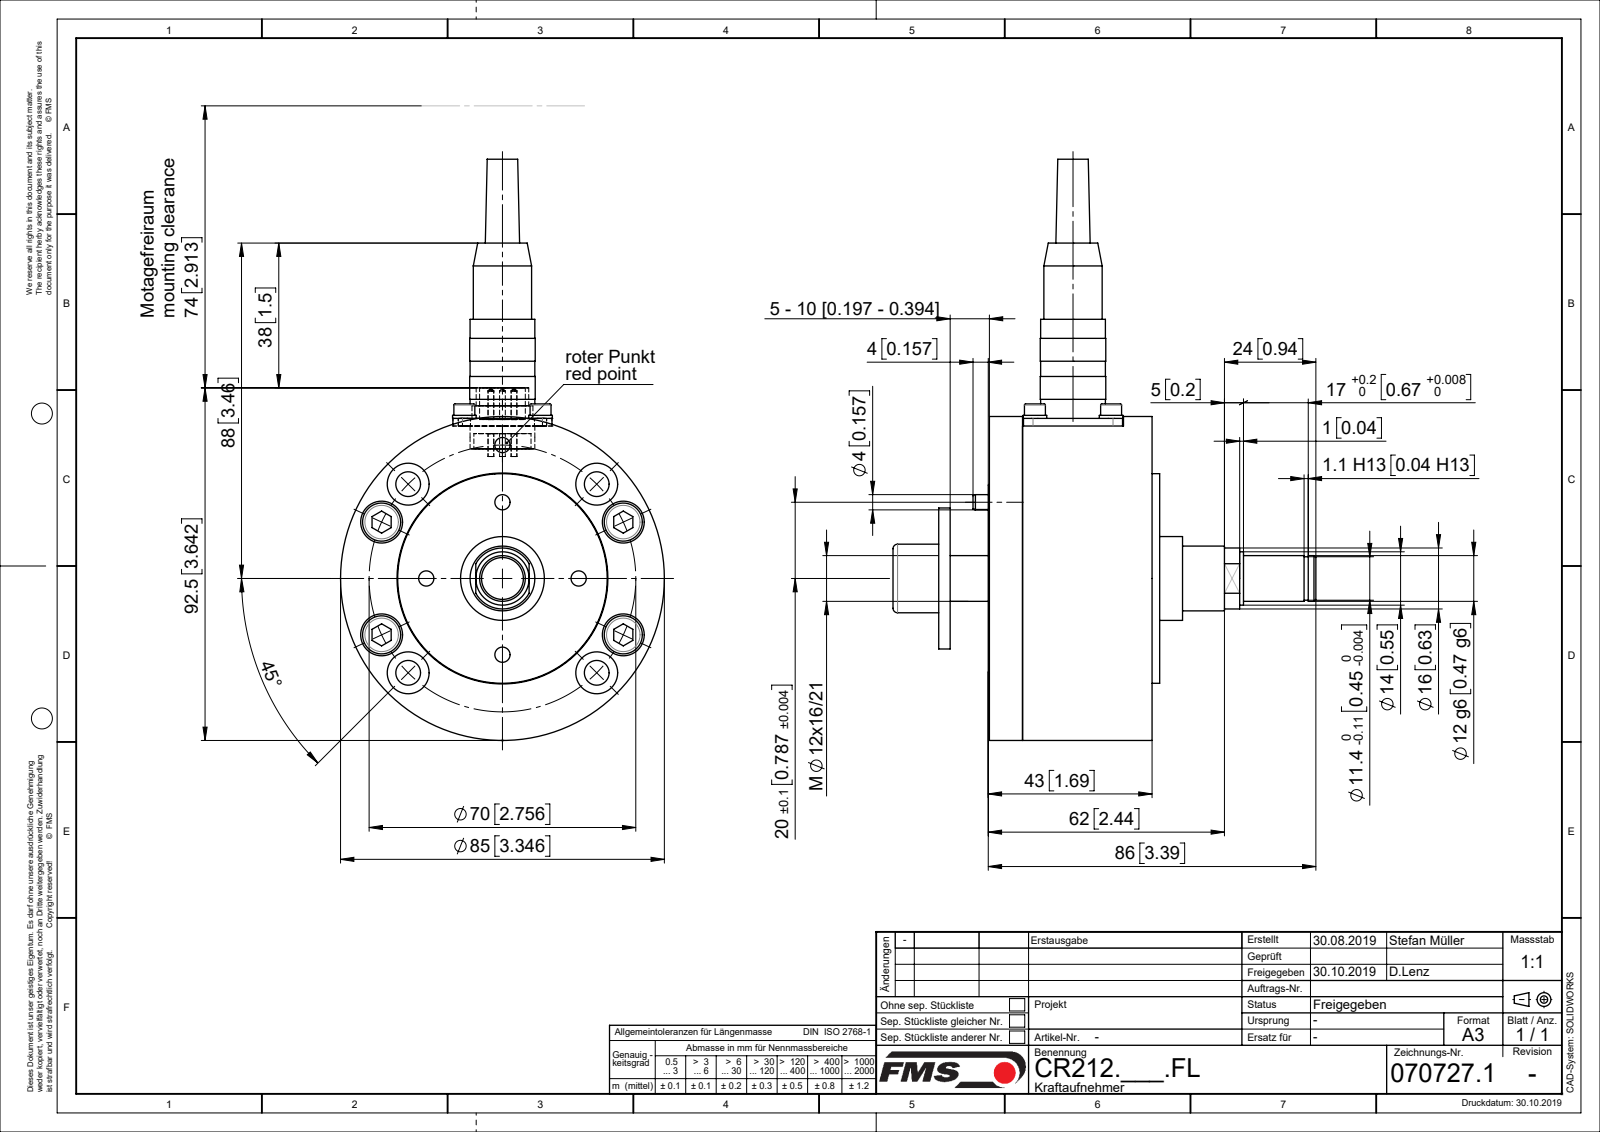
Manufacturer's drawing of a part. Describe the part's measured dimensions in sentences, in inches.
The part is named "ZEICHNUNG5; C0707271; C0709081; C0612056 (+8 more)". Its 3-D file was written by "Mechanical Desktop 2009 (CONFIG_CONTROL_DESIGN)". It is 26 solids with 485 faces: 150 planar, 249 cylindrical and 86 other. Overall it measures 6.004 by 4.409 by 3.346 inches. Its volume is 13.48 cubic inches and its surface area 131.2 square inches. Round holes: 8 of diameter 0.256, 8 of diameter 0.433, 4 of diameter 0.102, 4 of diameter 0.126, 4 of diameter 0.157, 4 of diameter 0.203, 4 of diameter 0.276, 1 of diameter 0.281, 1 of diameter 0.42, 1 of diameter 0.472, 1 of diameter 0.512, 1 of diameter 0.591. Round bosses or shafts: 5 of diameter 0.059, 4 of diameter 0.394, 4 of diameter 0.244, 4 of diameter 0.236, 4 of diameter 0.217, 4 of diameter 0.197, 4 of diameter 0.118, 2 of diameter 0.669. Partial cylindrical surfaces (rounded edges, fillets, slot ends): 4 of radius 0.098, 2 of radius 0.197, 1 of radius 0.315. The main face-to-face distances are 0.236, 0.118, 0.354, 1.772, 0.394, 0.079, 1.339, 1.693, 1.575, 1.654. The hole center spacings are 0.787, 0.992, 1.378, 2.013, 1.113, 0.479, 0.557, 0.743.
